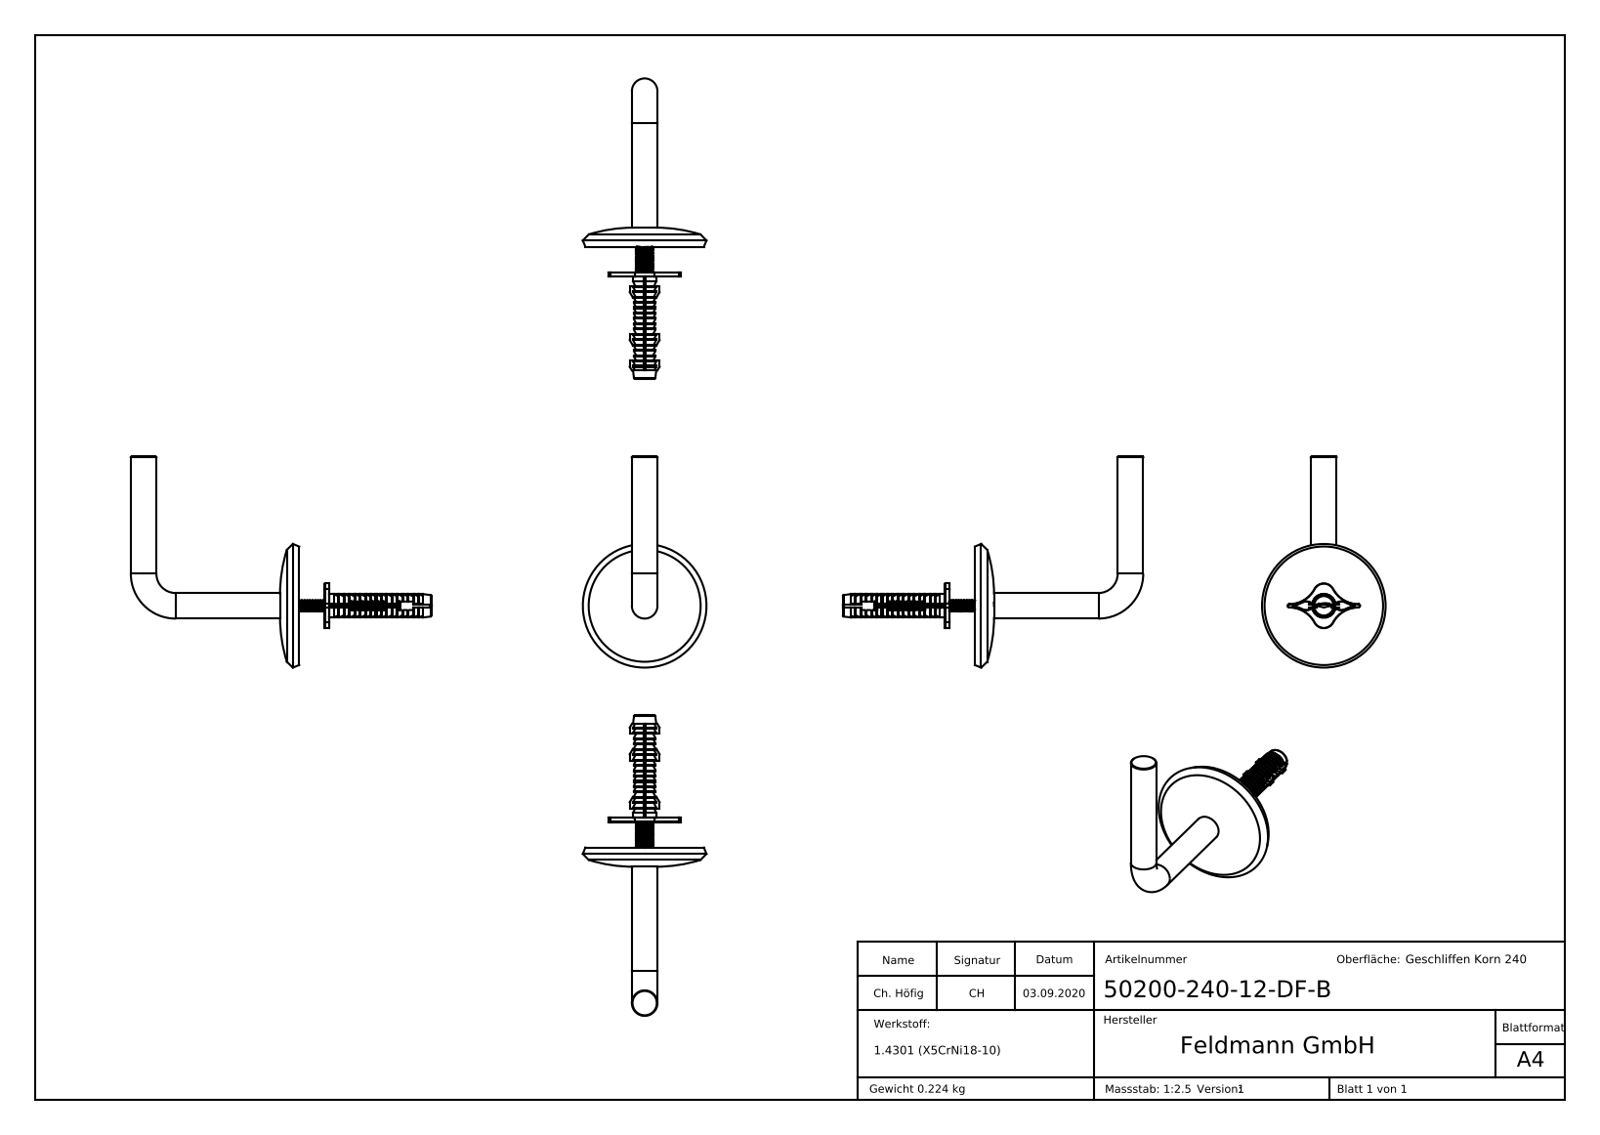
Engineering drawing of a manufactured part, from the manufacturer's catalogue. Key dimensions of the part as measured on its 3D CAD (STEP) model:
Part name (STEP PRODUCT): 50XXX-240-DF Teil3_Drehfix Dbel; 50XXX-240-DF Teil1_50XXX-240-DF Teil1; 50XXX-240-12-DF Teil5_50XXX-240-12-DF Teil5; 50XXX-240-DF Teil1 (+5 more)
STEP written by: SolidWorks 2018 (CONFIG_CONTROL_DESIGN)
Units: millimetres
Bodies: 4 solids, 3235 faces (603 planar, 350 cylindrical, 2282 other)
Overall size (bounding box): 141 × 99 × 58
Volume: 30 842 mm³ · Surface area: 18 296 mm²
Round holes (diameter × count): ⌀6.8 ×1, ⌀10.5 ×1
Round bosses / shafts (diameter × count): ⌀12 ×2, ⌀11 ×1, ⌀10 ×1
Partial cylindrical surfaces — rounded edges, fillets, slot ends (radius × count): R0.1 ×20, R4 ×8, R0.5 ×6, R1 ×4, R13.38 ×4, R80 ×4, R0.3 ×2, R0.8 ×2
Main face-to-face distances: 0.5, 3.5, 2.5, 4, 5, 3, 2, 1, 2.15, 1.35
